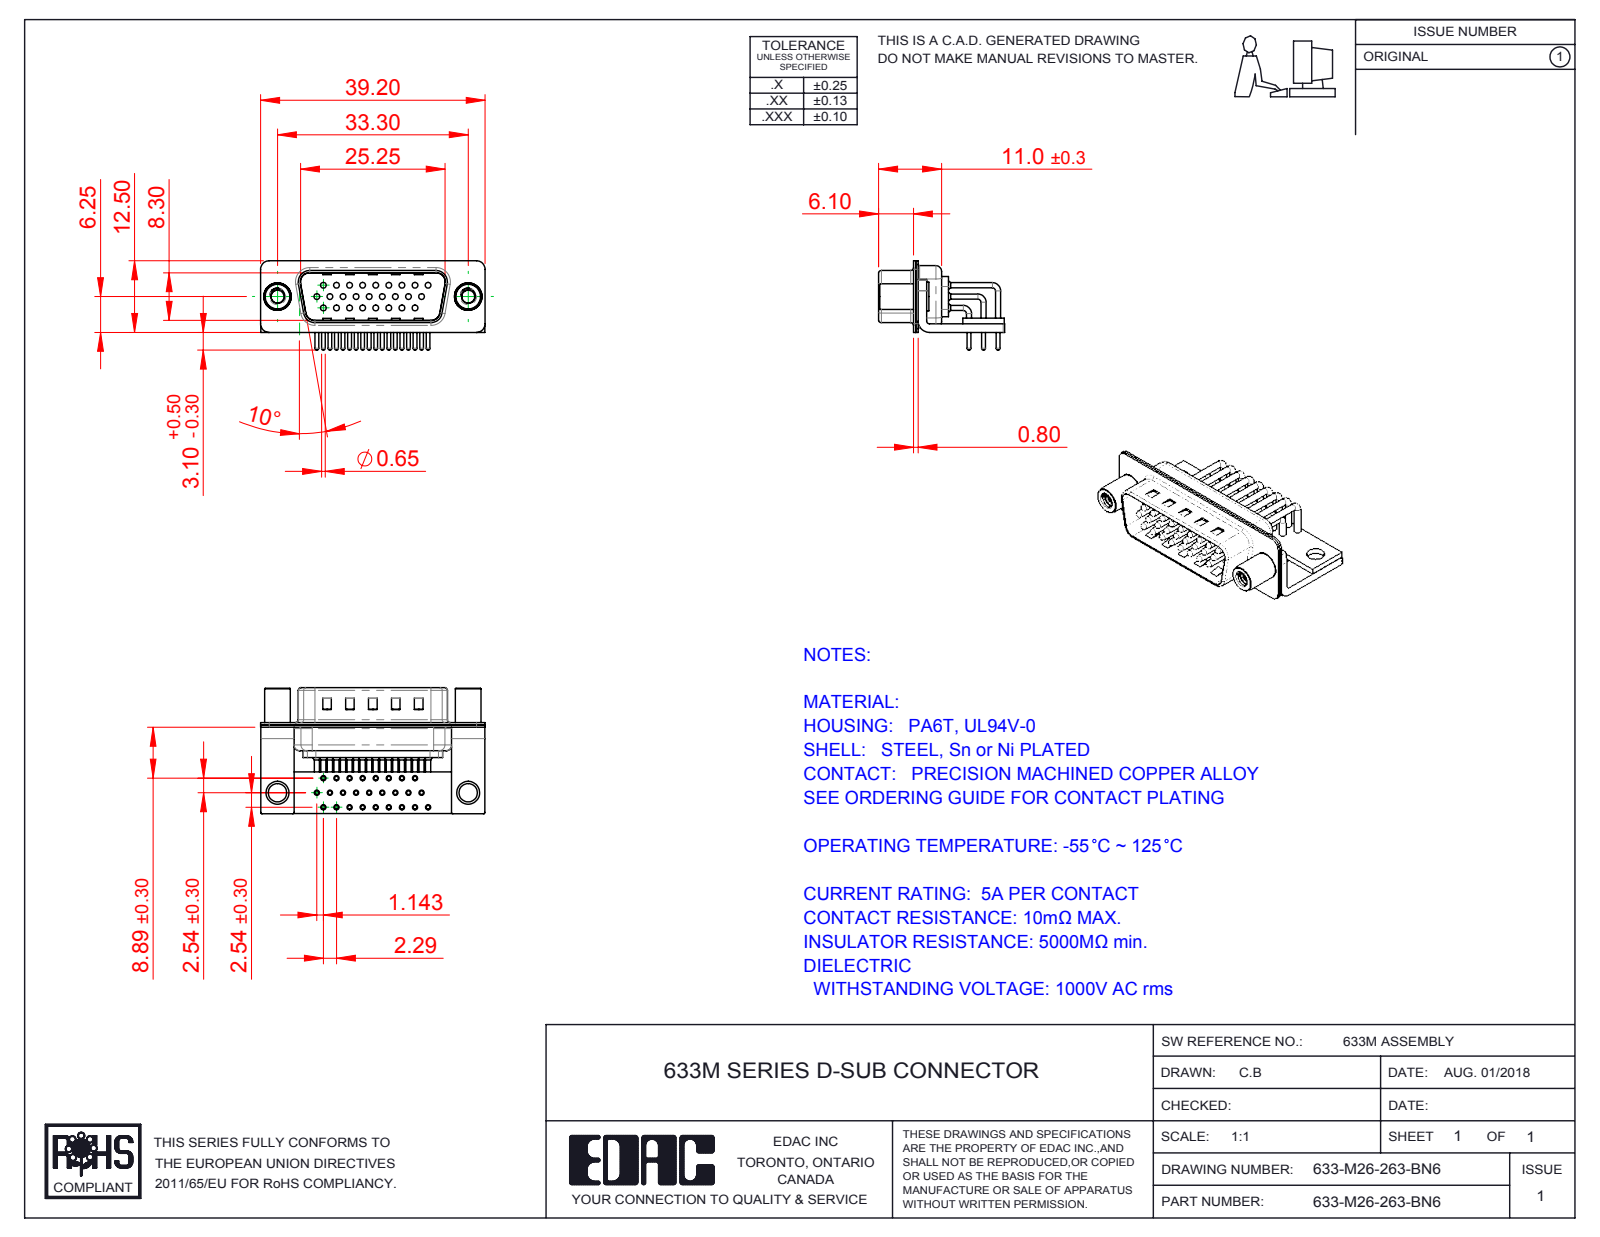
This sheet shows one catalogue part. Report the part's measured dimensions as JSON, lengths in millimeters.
{"part_name": "633-M26-263-BN6; 633M Housing_26 Contacts; 633M Contact Row 2; 633M Contact Row 3 (+6 more)", "step_written_by": "SolidWorks 2016 (CONFIG_CONTROL_DESIGN)", "units": "millimeters", "bodies": {"solids": 34, "faces": 3352, "planar": 1831, "cylindrical": 1185, "other": 336}, "overall_size": [39.2, 22, 15.6], "volume_mm3": 2748, "surface_area_mm2": 8315, "round_holes": [[0.9, 26], [1, 26], [1.7, 26], [2, 26], [2.26, 2], [3.2, 2], [4, 2], [4.8, 2]], "round_bosses_or_shafts": [[1.5, 26], [0.9, 26], [0.65, 26], [5, 2], [4.9, 2], [4.5, 2]], "partial_cylinders_radius": [[1.01, 26], [0.25, 16], [1.5, 16], [2, 13], [0.5, 9], [1.6, 8], [0.6, 4], [0.65, 4]], "face_to_face_distances": [0.4, 1.5, 0.85, 0.8, 1.25, 1, 1.9, 10.4, 9.55, 2.5], "hole_center_spacings": [4.57, 2.29, 2.28, 3.96, 6.86, 4.27, 6.05, 2.78]}
